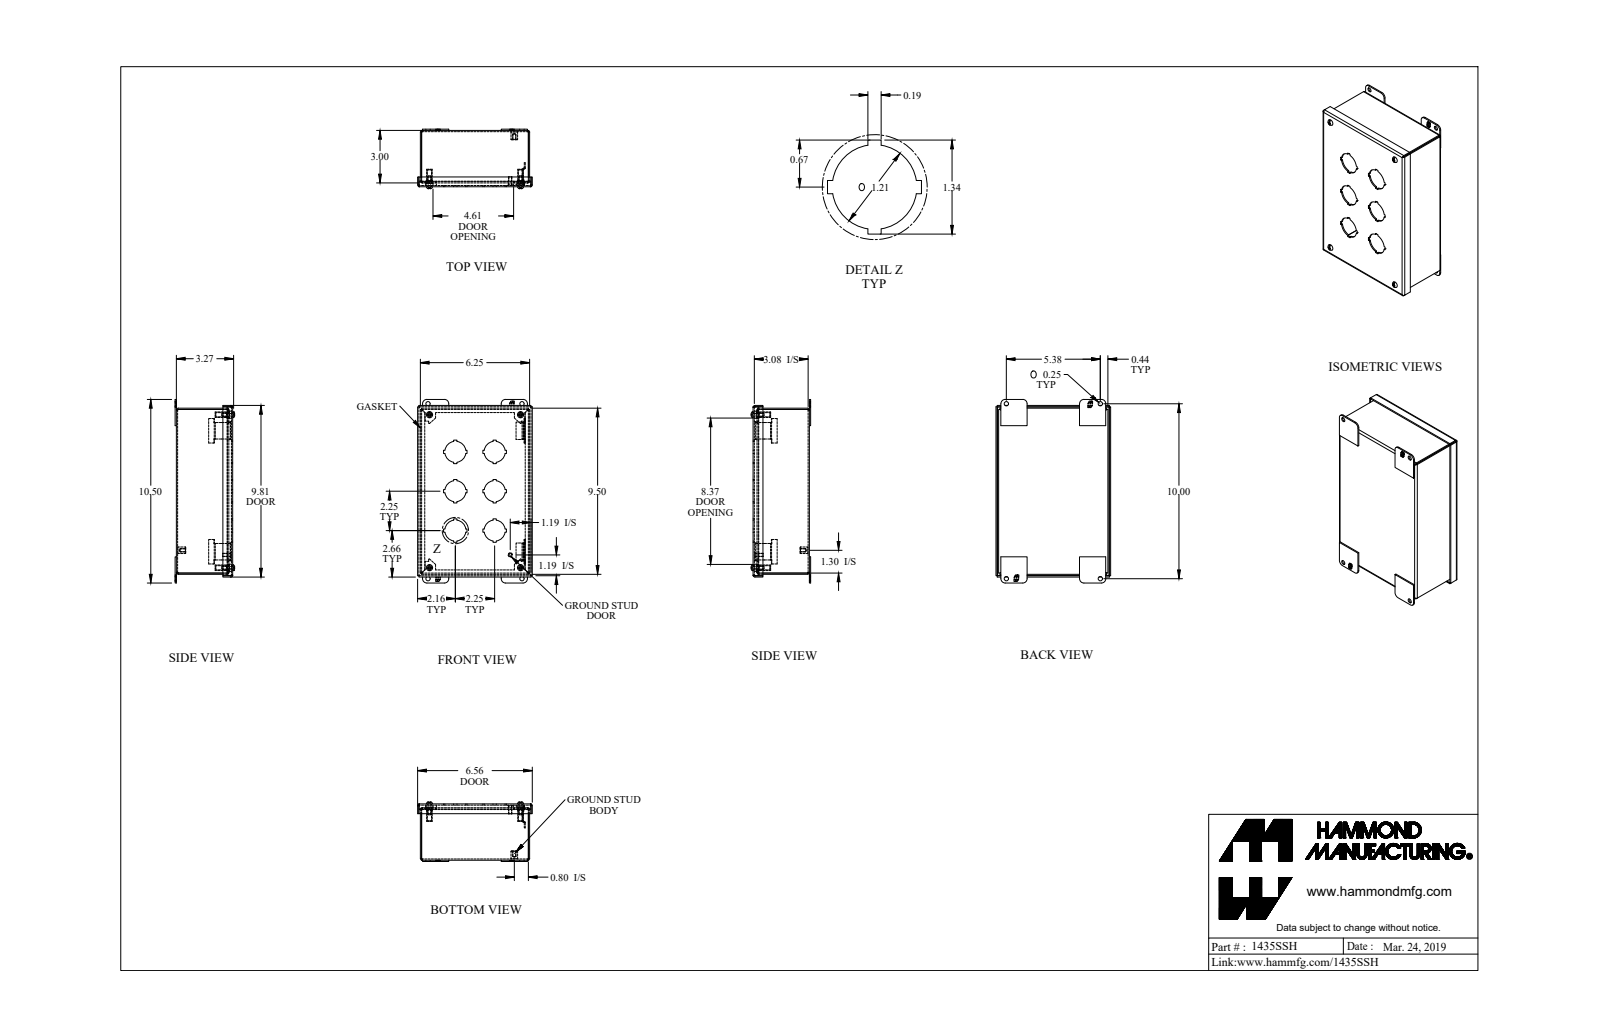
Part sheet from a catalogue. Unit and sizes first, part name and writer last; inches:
Units: inches
Overall size (bounding box): 10.5 × 6.562 × 3.404
Round holes (diameter × count): ⌀0.25 ×8, ⌀1.21 ×6, ⌀0.065 ×4, ⌀0.239 ×4, ⌀0.253 ×4, ⌀0.406 ×4, ⌀0.156 ×1
Round bosses / shafts (diameter × count): ⌀0.19 ×5, ⌀0.406 ×4, ⌀0.315 ×4, ⌀0.148 ×4, ⌀0.375 ×1, ⌀0.25 ×1
Partial cylindrical surfaces — rounded edges, fillets, slot ends (radius × count): R0.036 ×12, R0.108 ×12, R0.25 ×8, R0.029 ×4, R0.086 ×4, R0.171 ×4
Main face-to-face distances: 0.072, 3.15, 3.222, 3.078, 6.178, 9.428, 6.25, 6.106, 0.156, 6.334
Hole centre spacings: 5.211, 5.212, 2.25, 0.63, 8.749, 9.375, 10.183, 0.631
Volume: 20.39 in³ · Surface area: 540.4 in²
Bodies: 23 solids, 701 faces (495 planar, 176 cylindrical, 30 other)
Part name (STEP PRODUCT): 1435SSH_Default
STEP written by: SolidWorks 2019 (CONFIG_CONTROL_DESIGN)
